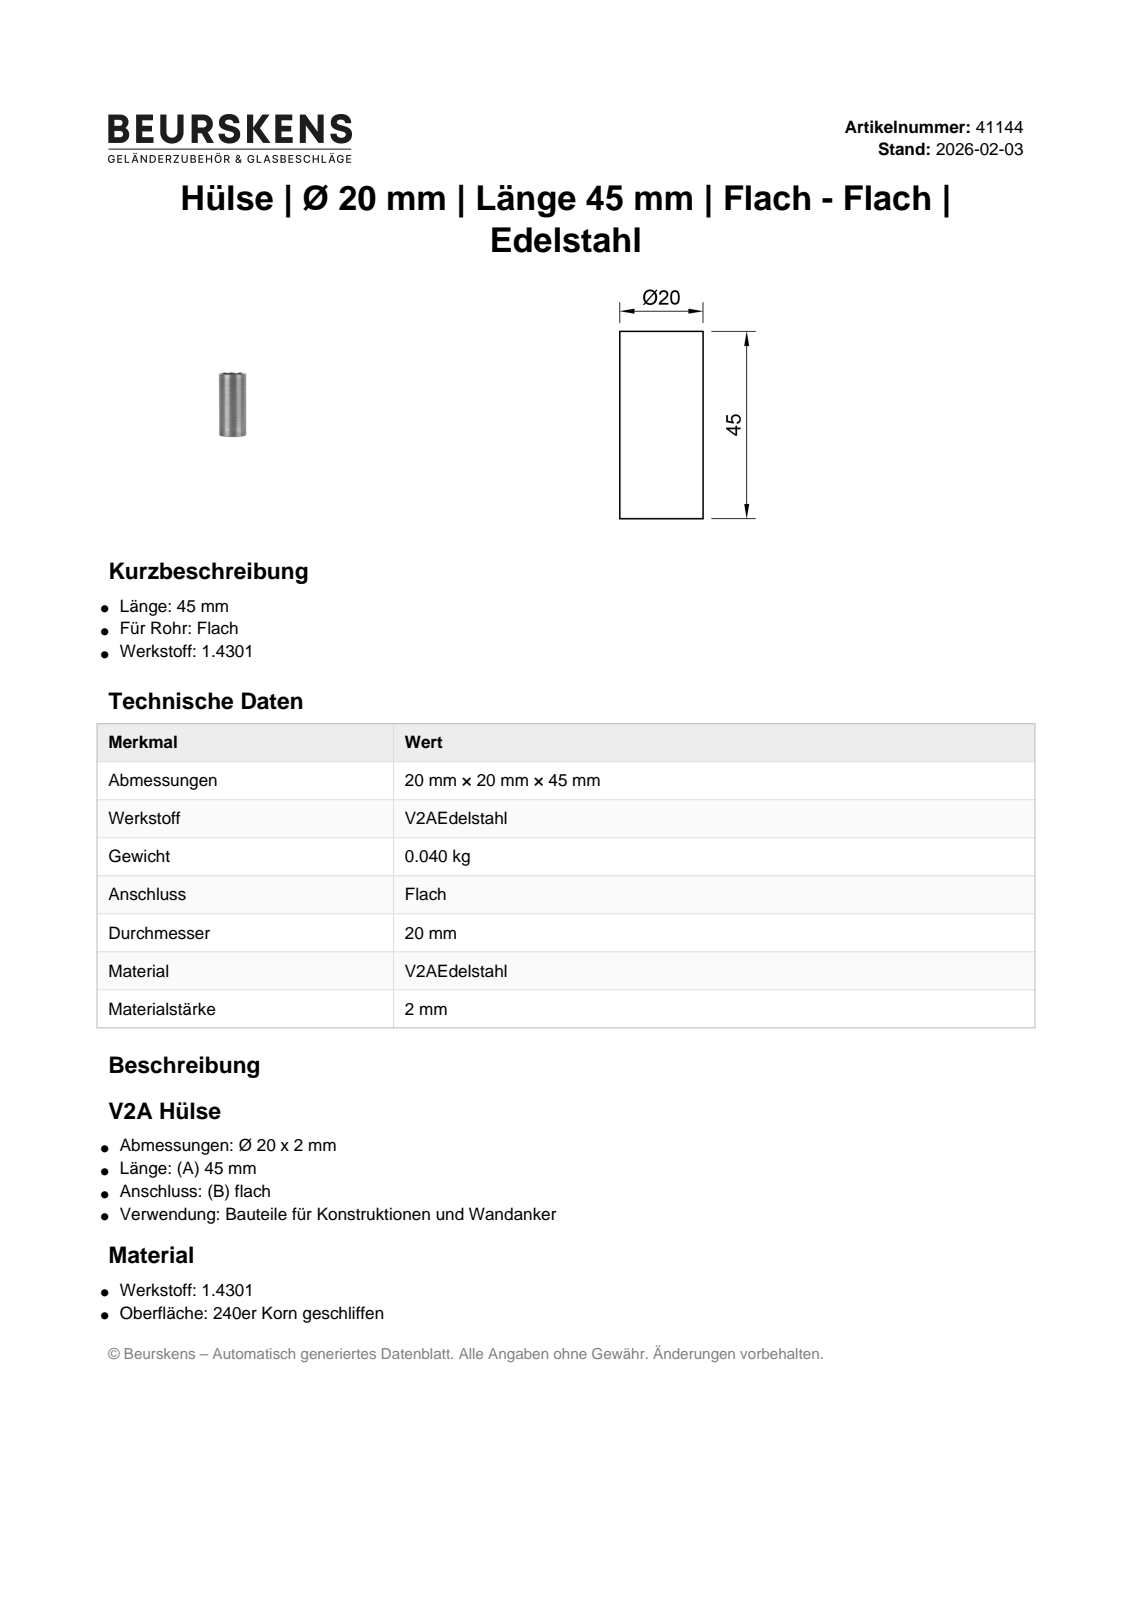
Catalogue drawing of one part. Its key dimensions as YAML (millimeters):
part_name: "41144"
step_written_by: "Autodesk Inventor 2022 (AUTOMOTIVE_DESIGN)"
units: millimeters
bodies: {solids: 1, faces: 4, planar: 2, cylindrical: 2, other: 0}
overall_size: [45, 20, 20]
volume: 2686
surface_area: 5492
round_holes:
  - {diameter: 18, count: 1}
round_bosses_or_shafts:
  - {diameter: 20, count: 1}
face_to_face_distances: [45]
